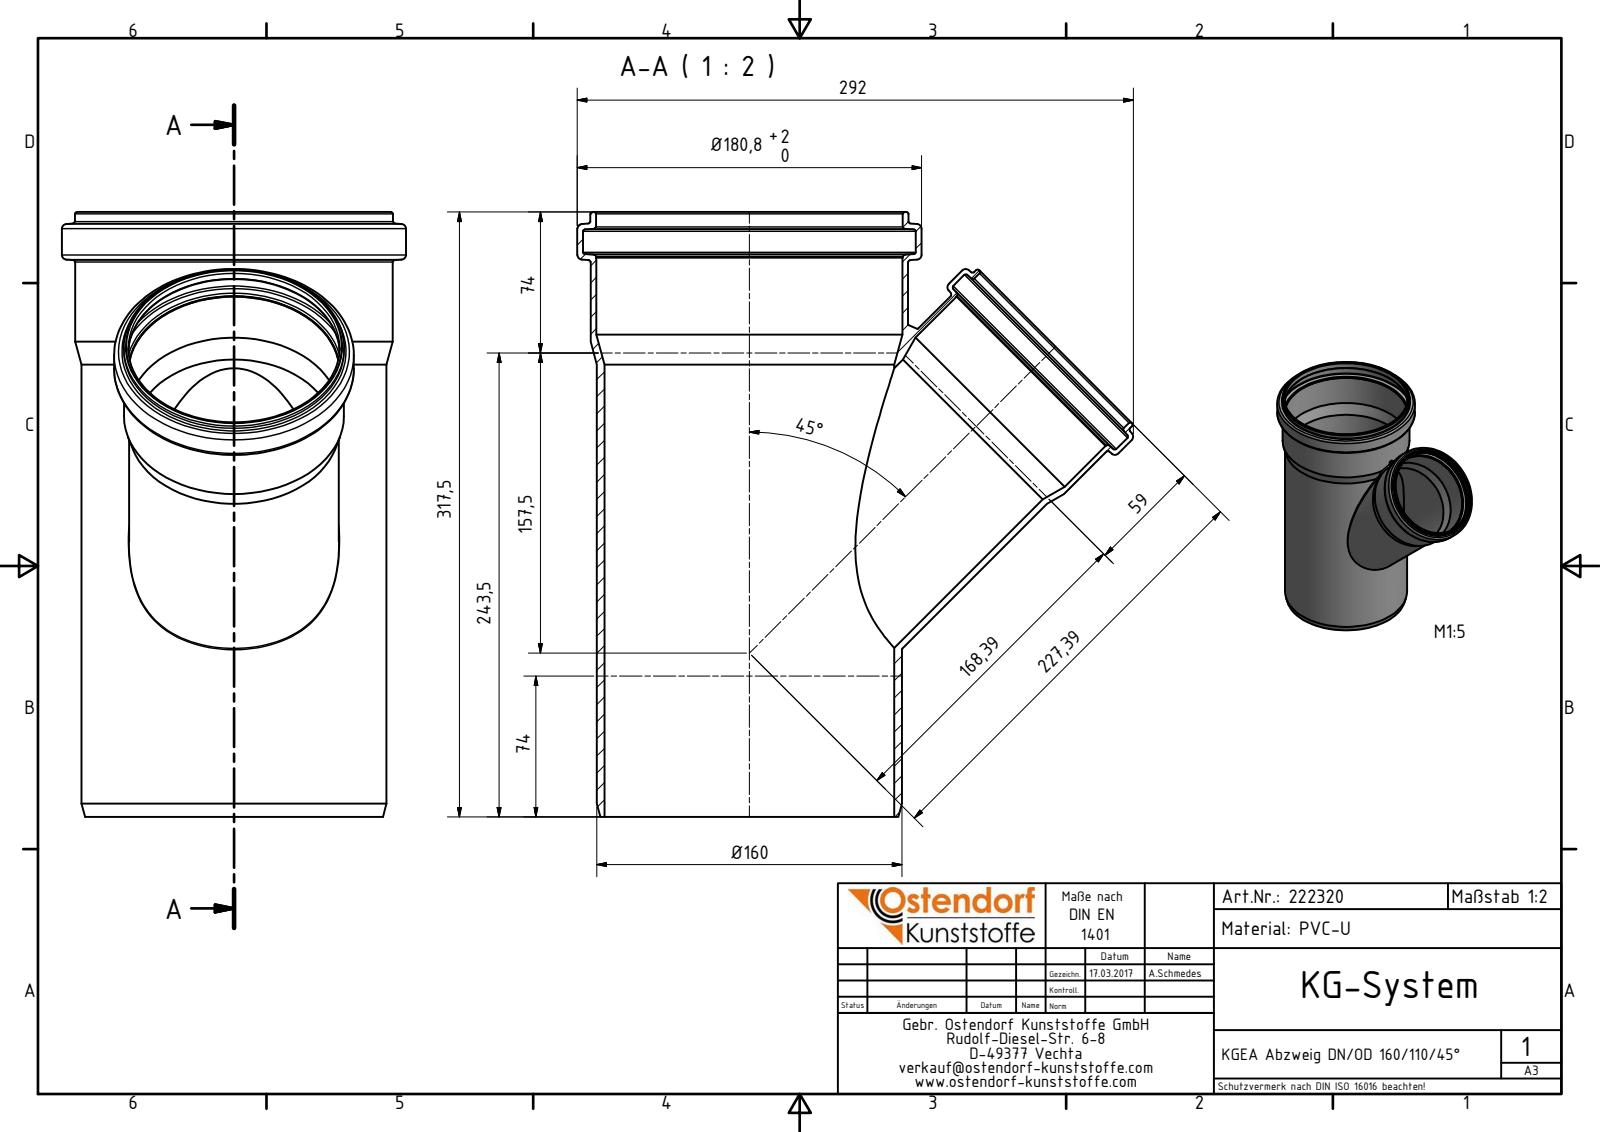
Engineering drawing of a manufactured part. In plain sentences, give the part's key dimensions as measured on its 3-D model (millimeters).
The part is named "222320 KGEA Abzweig DN_OD 160_110_45°". Its 3-D file was written by "Autodesk Inventor 2016 (AUTOMOTIVE_DESIGN)". It is 1 solid with 78 faces: 8 planar, 24 cylindrical and 46 other. Overall it measures 317.5 by 292 by 180.8 millimeters. Its volume is 698 594 cubic millimeters and its surface area 400 624 square millimeters. Round holes: 2 of diameter 111, 1 of diameter 103.8, 1 of diameter 110.7, 1 of diameter 121.1, 1 of diameter 152.2, 1 of diameter 160.7, 1 of diameter 161.1, 1 of diameter 174.8. Round bosses or shafts: 1 of diameter 180.8, 1 of diameter 167.1, 1 of diameter 166.7, 1 of diameter 160.2, 1 of diameter 125.9, 1 of diameter 115.8, 1 of diameter 115.5, 1 of diameter 110.2. Partial cylindrical surfaces (rounded edges, fillets, slot ends): 6 of radius 0.5. The main face-to-face distances are 317.5, 293.53, 23.97, 18.21, 4.
